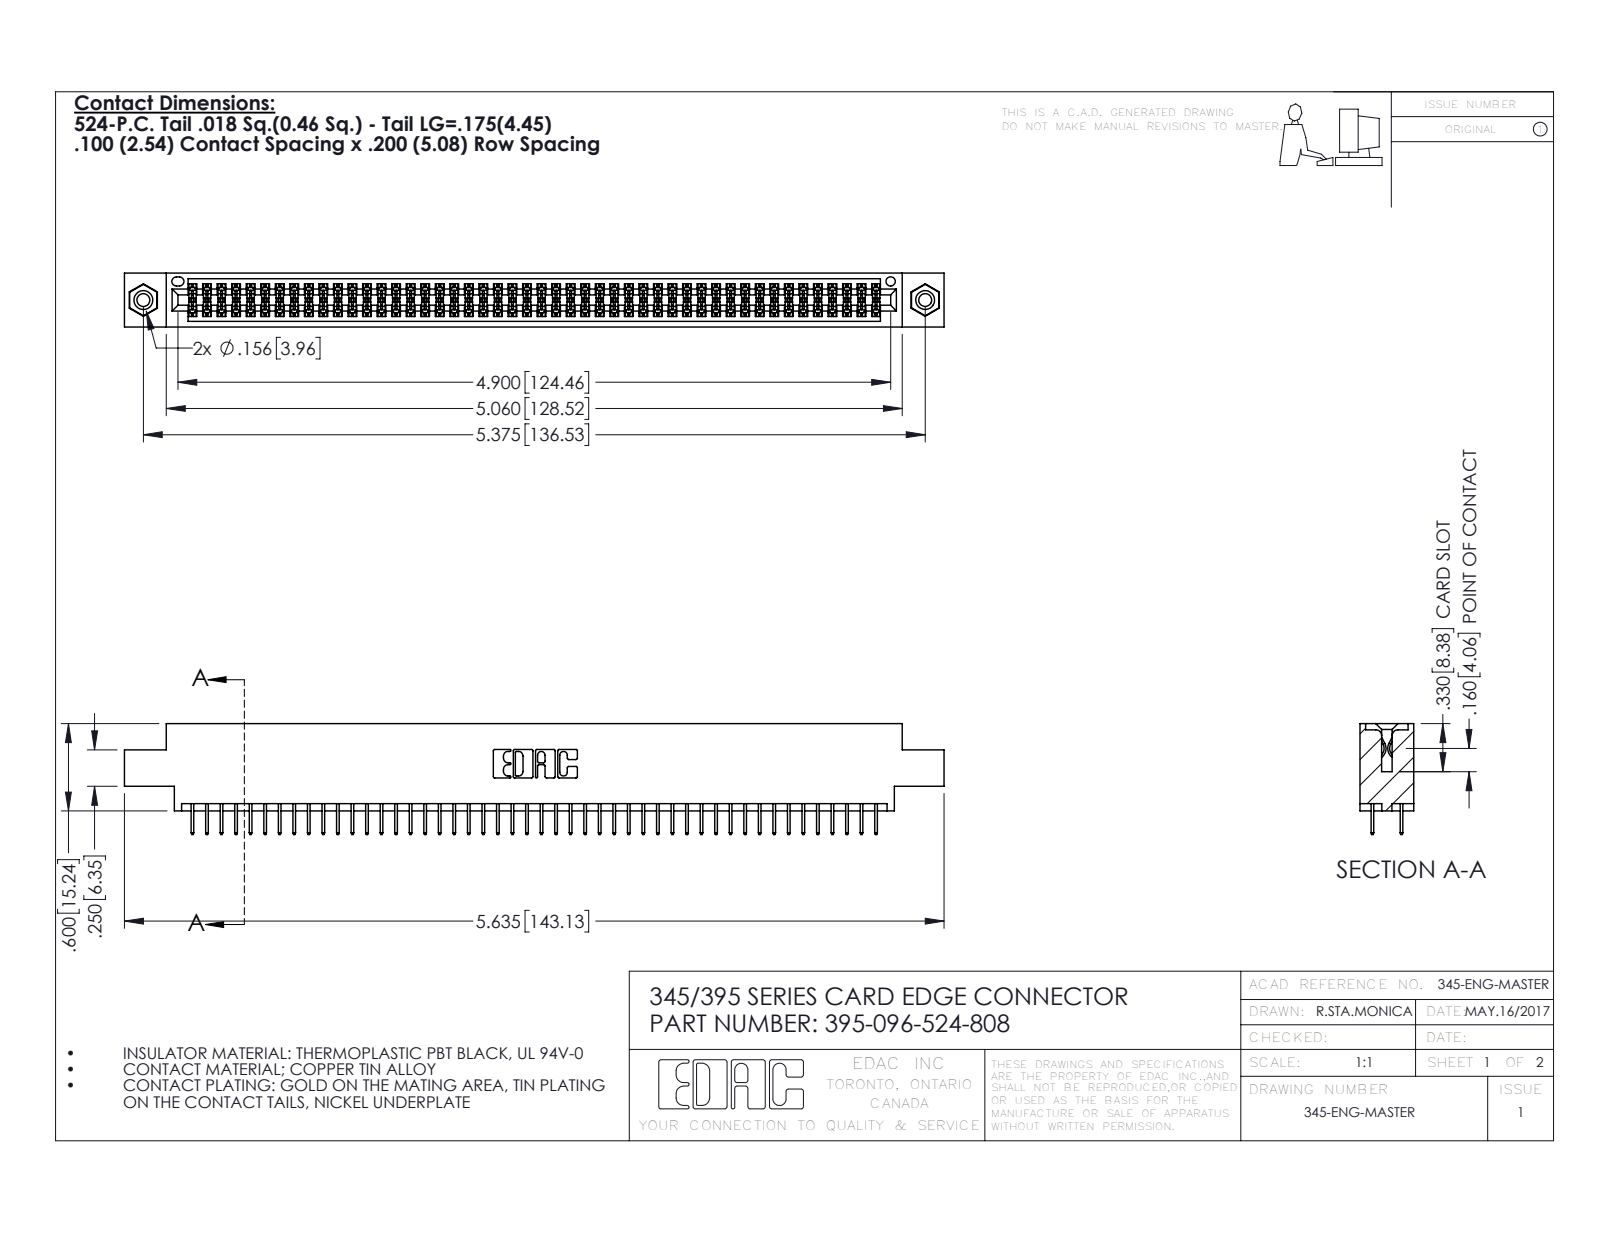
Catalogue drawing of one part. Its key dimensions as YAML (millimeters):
part_name: "345 Part_0.170 Offset - 0.156 Dia-TI; 345-292-001_345-293-124; 345-250-001_345-250-003-102; 395-096-524-808"
step_written_by: "SolidWorks 2016 (CONFIG_CONTROL_DESIGN)"
units: millimeters
bodies: {solids: 99, faces: 5374, planar: 3860, cylindrical: 1498, other: 16}
overall_size: [143.1, 19.4, 9.4]
volume: 13700
surface_area: 20130
round_holes:
  - {diameter: 2.3, count: 2}
  - {diameter: 3.2, count: 2}
  - {diameter: 4, count: 2}
  - {diameter: 1.6, count: 1}
round_bosses_or_shafts:
  - {diameter: 3.9, count: 2}
partial_cylinders:
  - {radius: 0.2, count: 144}
  - {radius: 0.3, count: 22}
  - {radius: 0.2, count: 6}
  - {radius: 0.8, count: 6}
  - {radius: 0.7, count: 3}
  - {radius: 0.4, count: 2}
  - {radius: 0.5, count: 2}
  - {radius: 0.6, count: 2}
face_to_face_distances: [1.8, 7.6, 9.4, 5.1, 2.5, 6.9, 0.6, 5.7, 4.4, 1.8]
hole_center_spacings: [6.9, 130.5, 136.5]
